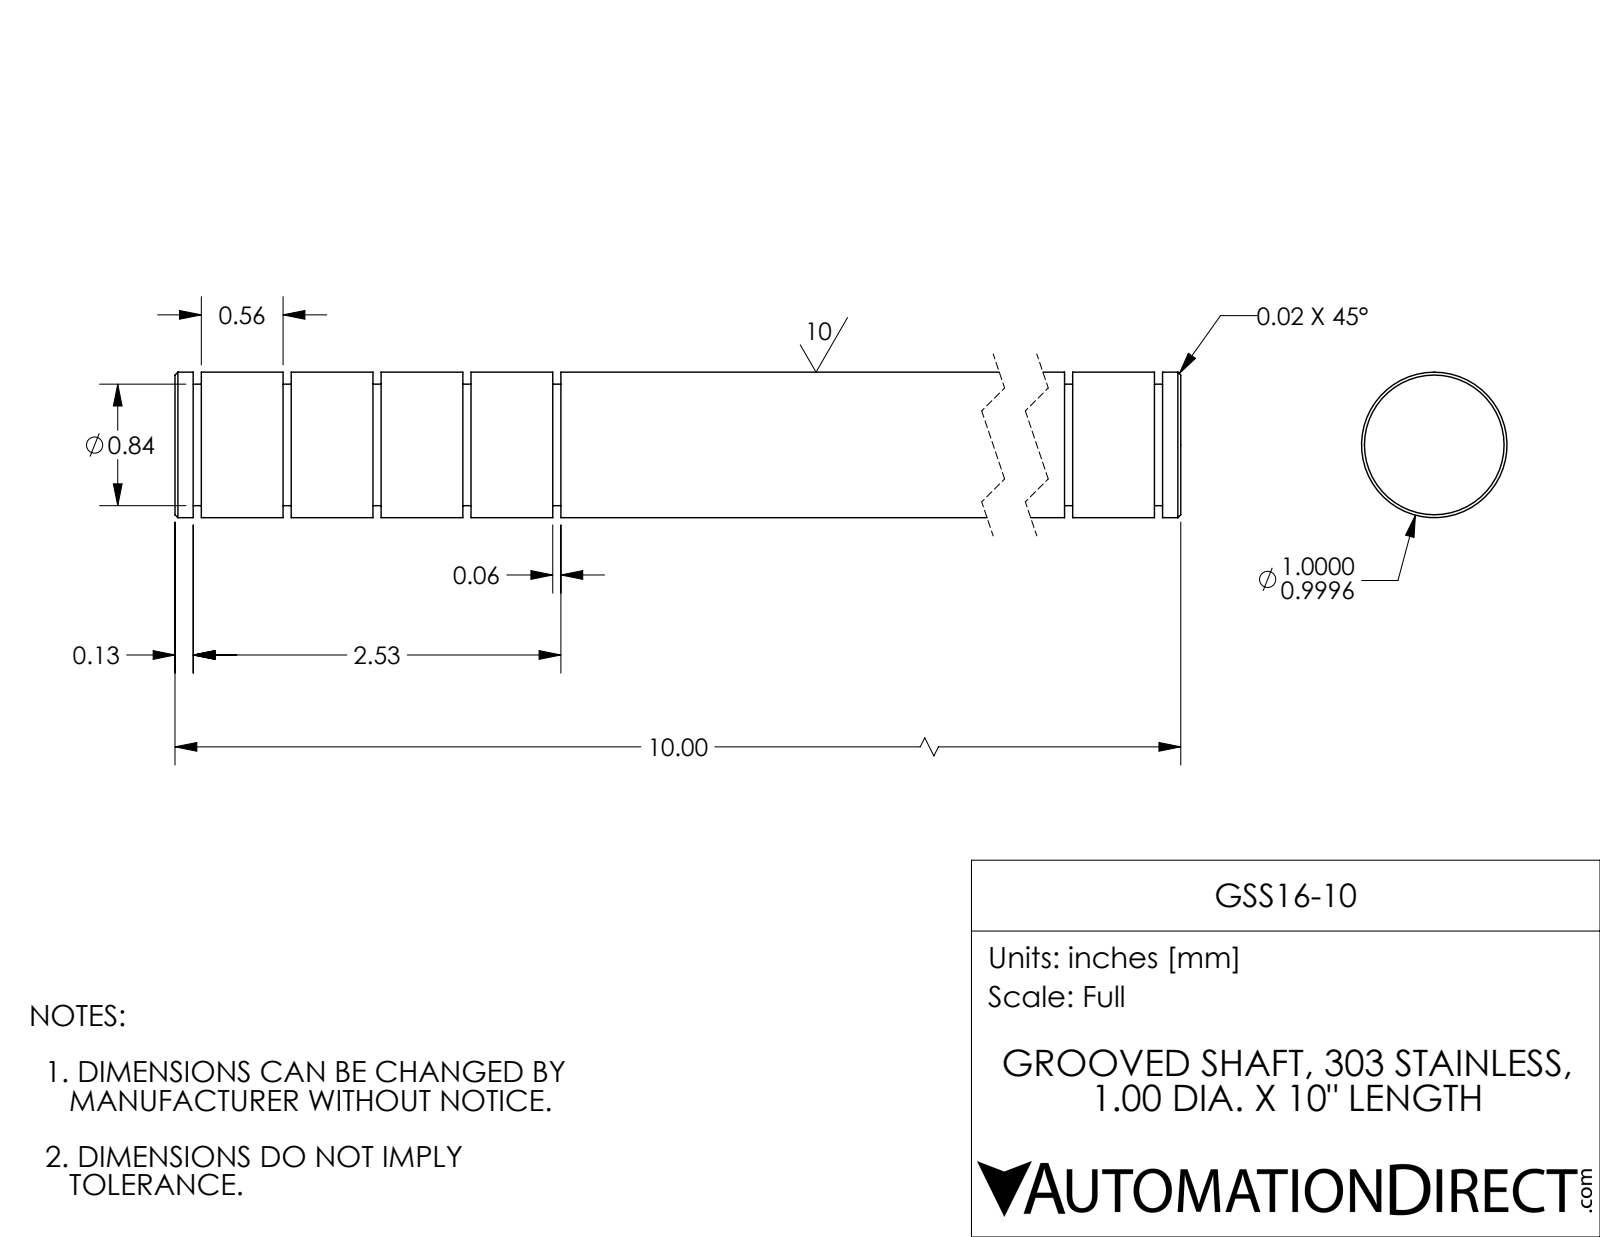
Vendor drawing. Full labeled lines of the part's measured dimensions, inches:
Part name (STEP PRODUCT): GSS16-10
STEP written by: SolidWorks 2017 (AUTOMOTIVE_DESIGN)
Units: inches
Bodies: 1 solid, 50 faces (16 planar, 30 cylindrical, 4 other)
Overall size (bounding box): 10 × 1 × 1
Volume: 7.76 in³ · Surface area: 36.04 in²
Round bosses / shafts (diameter × count): ⌀1 ×1, ⌀0.835 ×1
Main face-to-face distances: 0.618, 0.056, 0.618, 0.674, 1.236, 10, 7.222, 1.292, 0.562, 9.076
